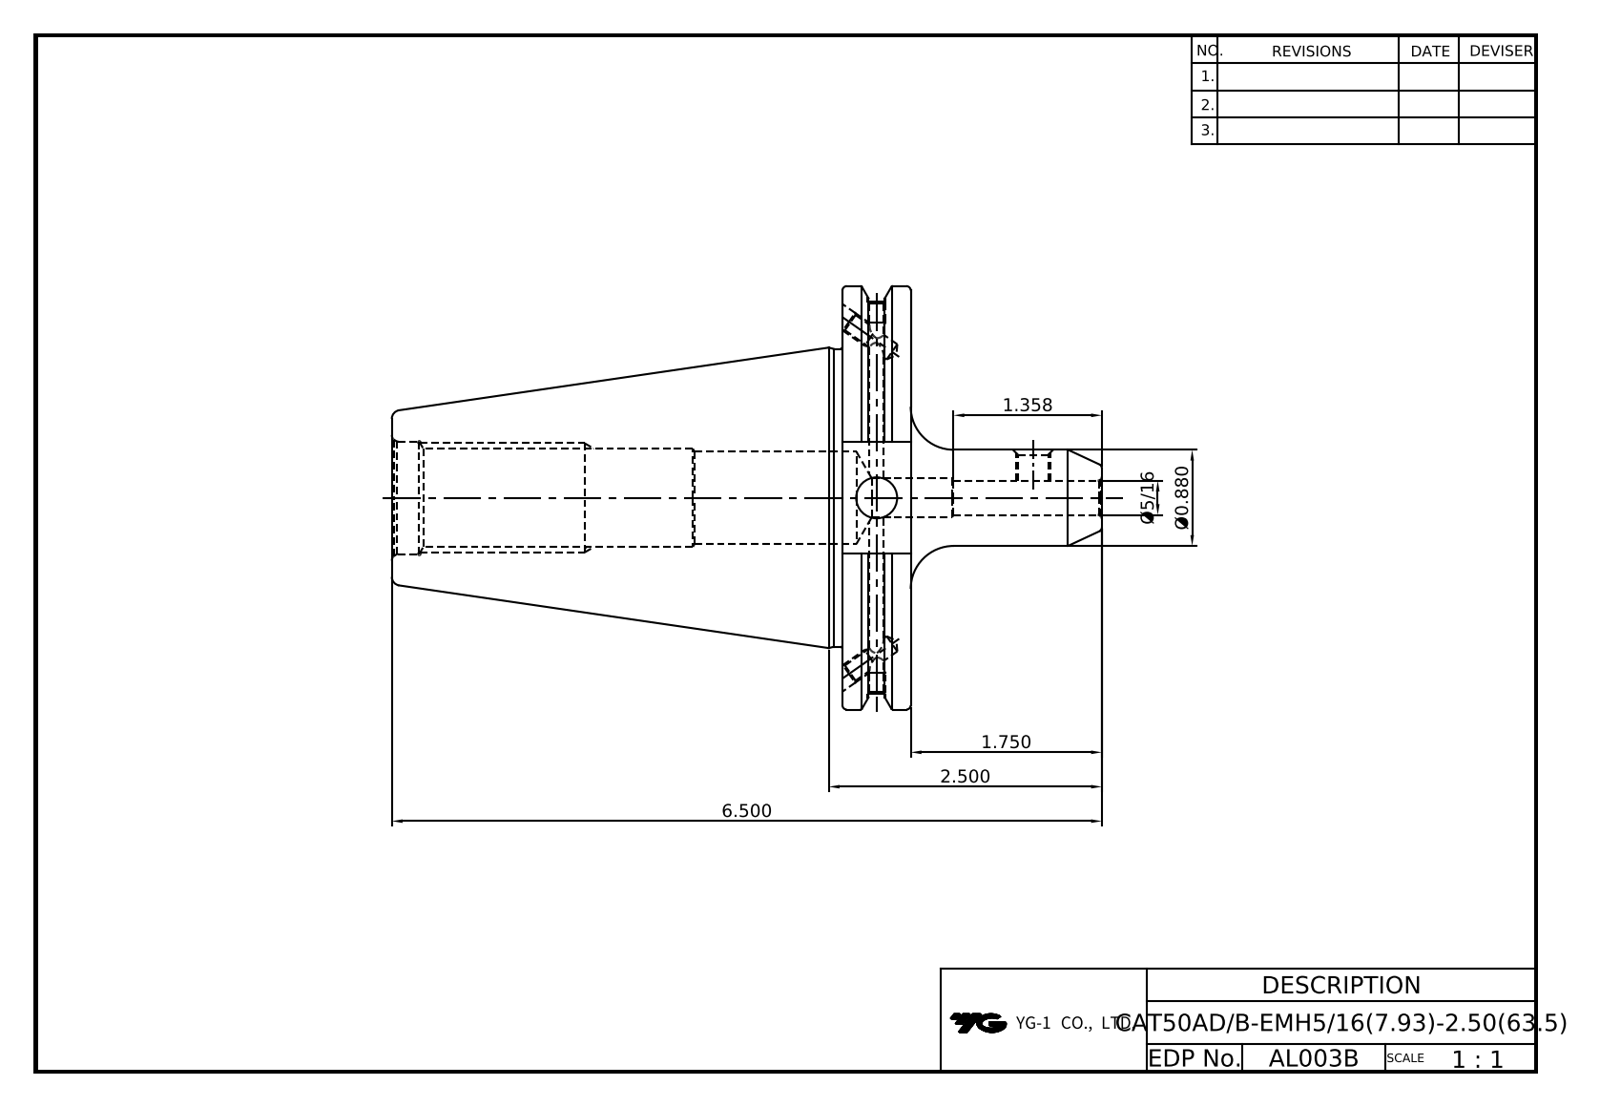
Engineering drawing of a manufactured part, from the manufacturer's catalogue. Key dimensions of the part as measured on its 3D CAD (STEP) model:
Part name (STEP PRODUCT): LO-CAT50ADB-EMH7.9375-63.5
STEP written by: Autodesk Inventor 2025 (AUTOMOTIVE_DESIGN)
Units: millimetres
Bodies: 1 solid, 86 faces (36 planar, 26 cylindrical, 24 other)
Overall size (bounding box): 165.1 × 98.42 × 94.69
Volume: 337 563 mm³ · Surface area: 48 615 mm²
Round holes (diameter × count): ⌀3.24 ×2, ⌀4.13 ×2, ⌀4.2 ×2, ⌀5 ×2, ⌀6.78 ×1, ⌀7.94 ×1, ⌀9 ×1, ⌀9.53 ×1, ⌀21.97 ×1, ⌀26.2 ×1
Round bosses / shafts (diameter × count): ⌀98.42 ×1, ⌀91.29 ×1, ⌀69.25 ×1, ⌀22.35 ×1
Main face-to-face distances: 15.88, 104.77, 120.65, 73.03, 25.9, 110.82, 6.05, 9.83, 114.65, 9.88
